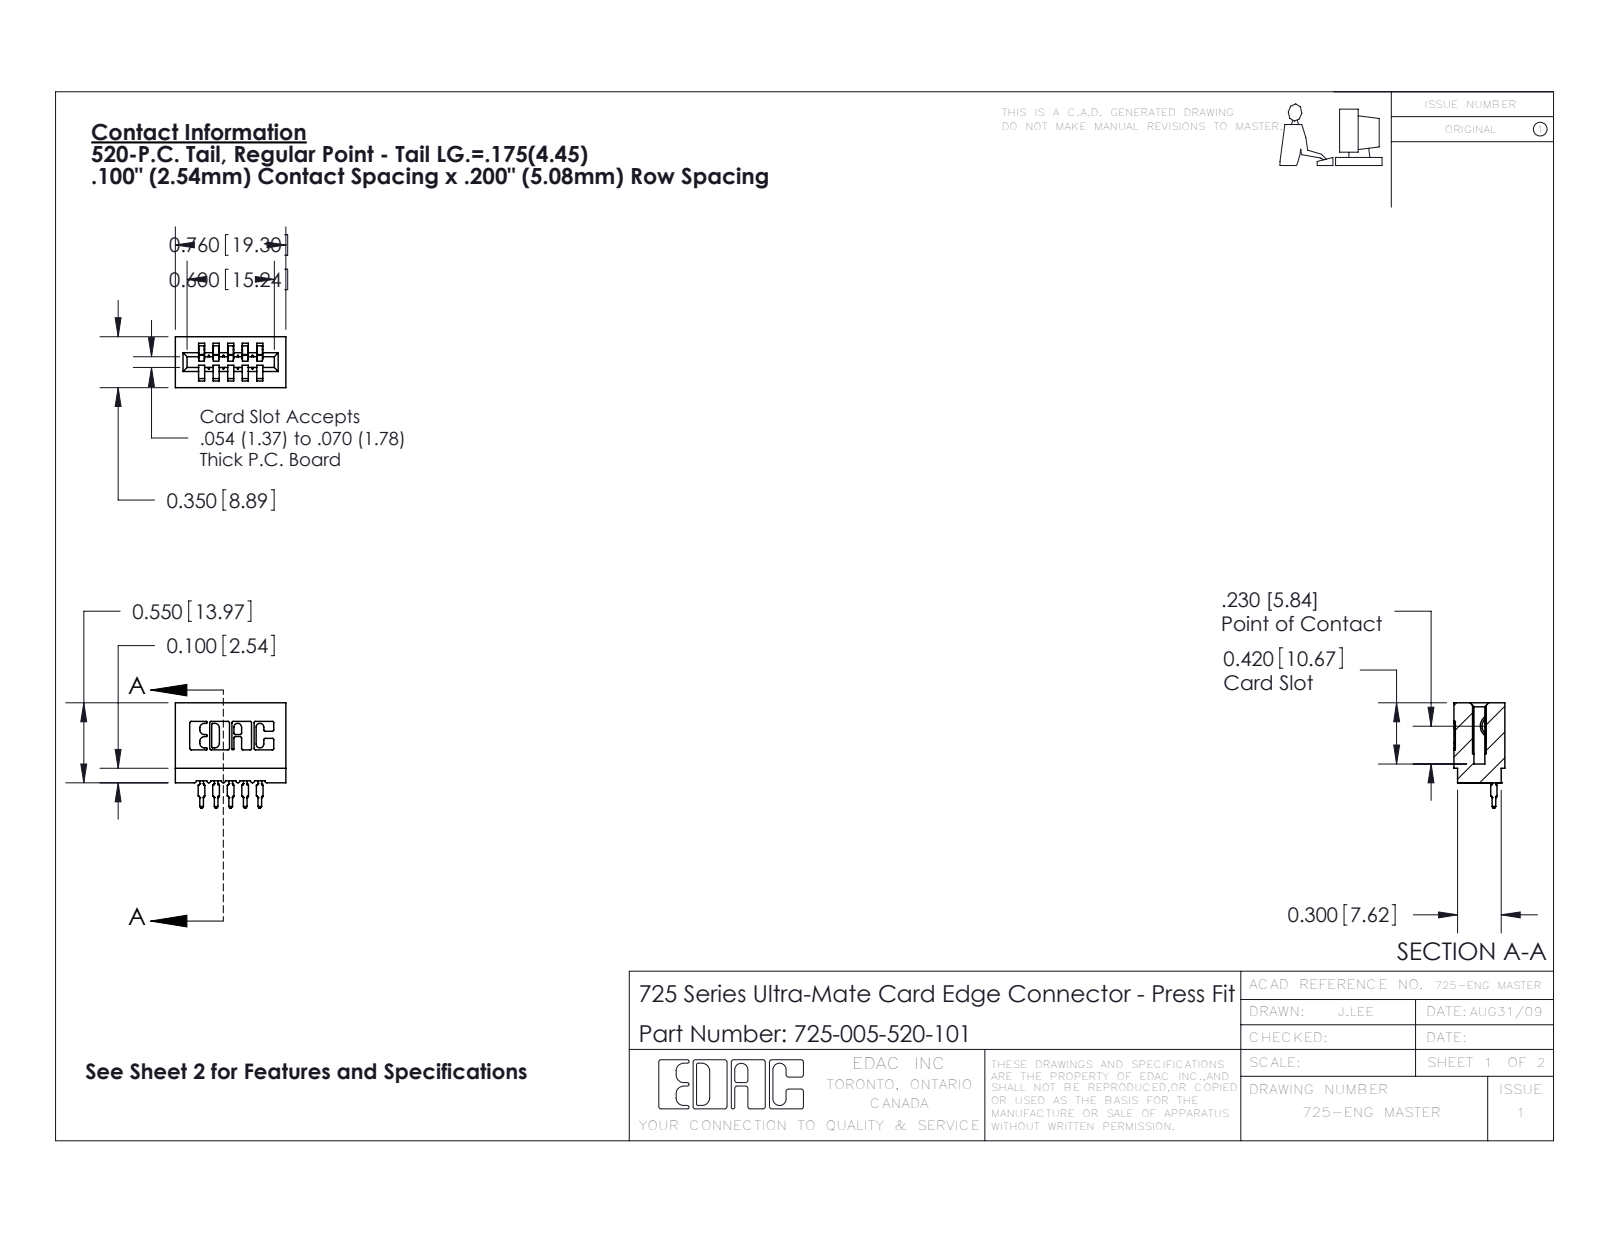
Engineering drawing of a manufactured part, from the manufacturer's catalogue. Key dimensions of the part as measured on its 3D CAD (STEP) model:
Part name (STEP PRODUCT): 745-292-001_520; 725 Part_Insulator Option - 01; 725-005-520-101
STEP written by: SolidWorks 2016 (CONFIG_CONTROL_DESIGN)
Units: inches
Bodies: 6 solids, 655 faces (390 planar, 135 cylindrical, 130 other)
Overall size (bounding box): 0.76 × 0.725 × 0.35
Volume: 0.102 in³ · Surface area: 3.874 in²
Partial cylindrical surfaces — rounded edges, fillets, slot ends (radius × count): R0.01 ×22, R0.015 ×10, R0.021 ×10, R0.007 ×6, R0.031 ×6, R0.005 ×4, R0.011 ×4, R0.026 ×3
Main face-to-face distances: 0.1, 0.2, 0.042, 0.058, 0.142, 0.3, 0.158, 0.242, 0.212, 0.35
